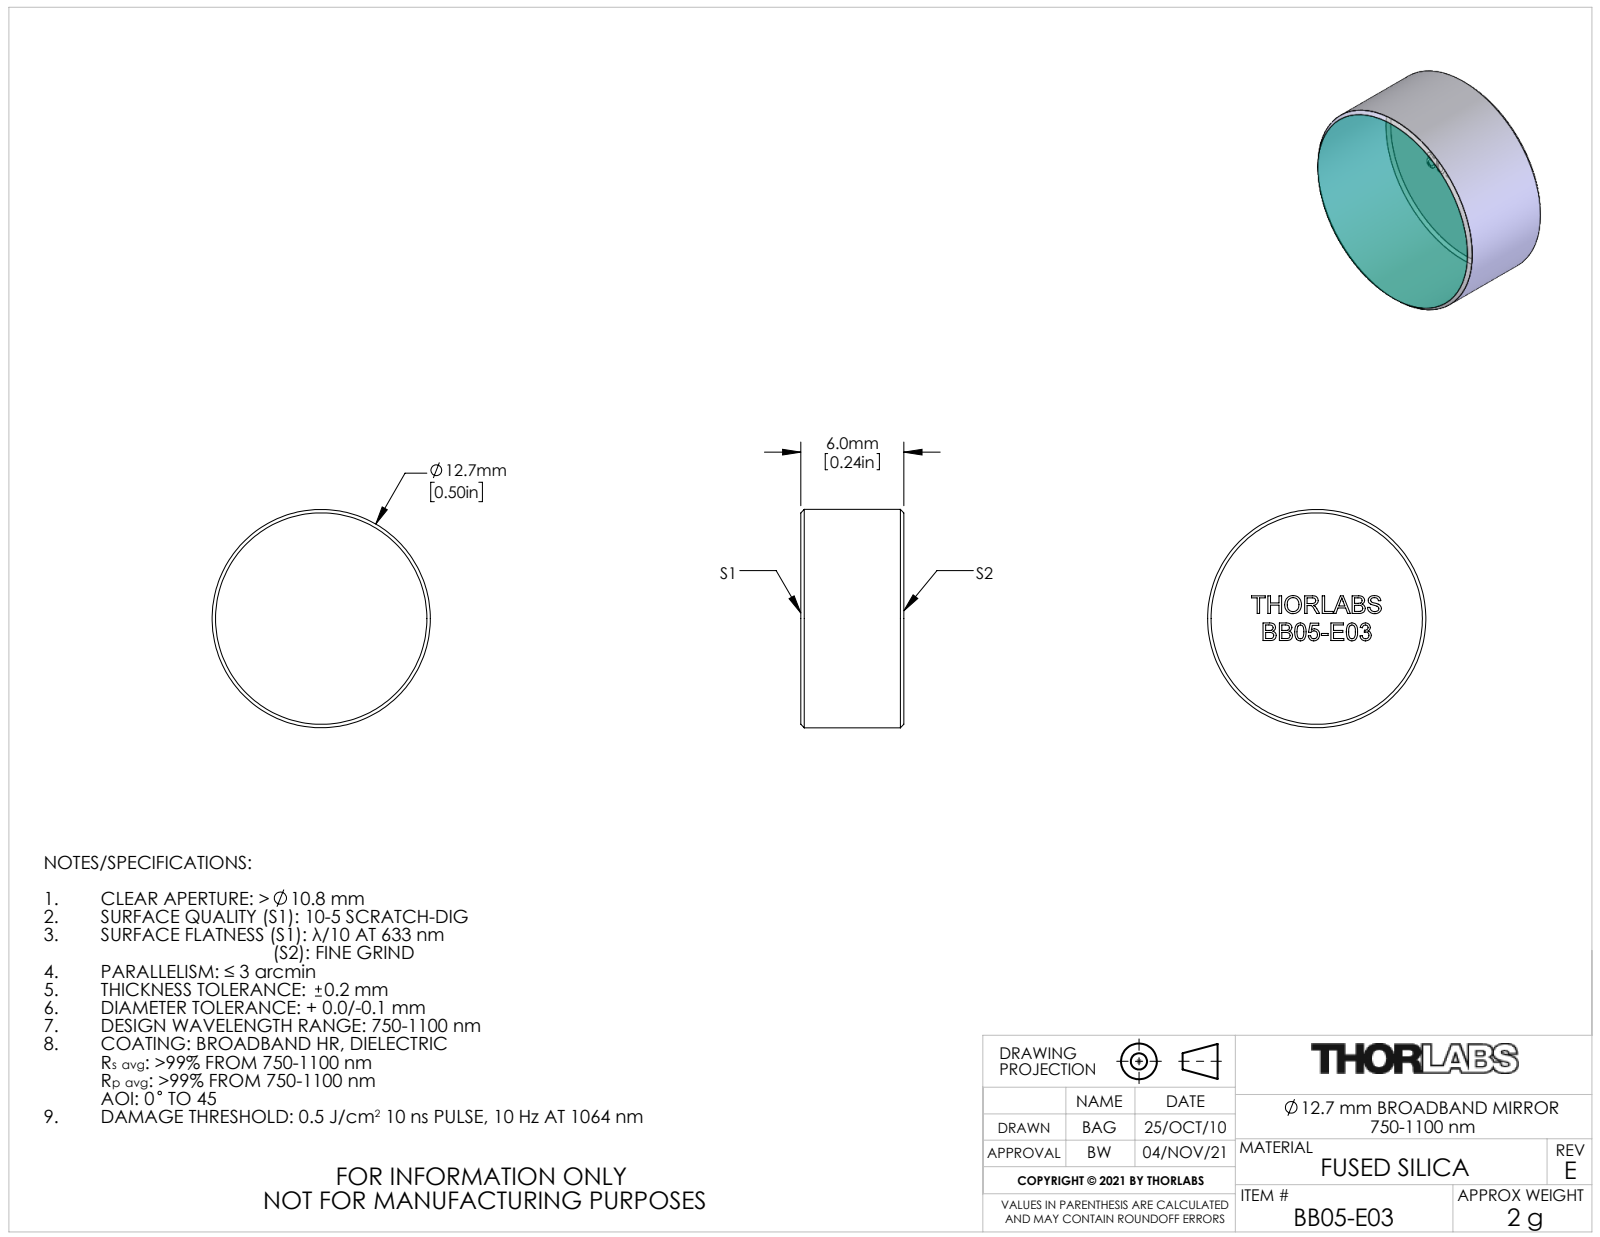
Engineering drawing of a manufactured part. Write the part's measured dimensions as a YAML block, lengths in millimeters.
part_name: "3543-E0W"
step_written_by: "SolidWorks 2016 (CONFIG_CONTROL_DESIGN)"
units: millimeters
bodies: {solids: 1, faces: 243, planar: 132, cylindrical: 2, other: 109}
overall_size: [12.7, 12.7, 6]
volume: 750
surface_area: 483
round_bosses_or_shafts:
  - {diameter: 12.7, count: 1}
face_to_face_distances: [6, 1, 1.6, 0.8, 0.9, 1.4, 1.3, 2.5, 0.5, 0.4]
